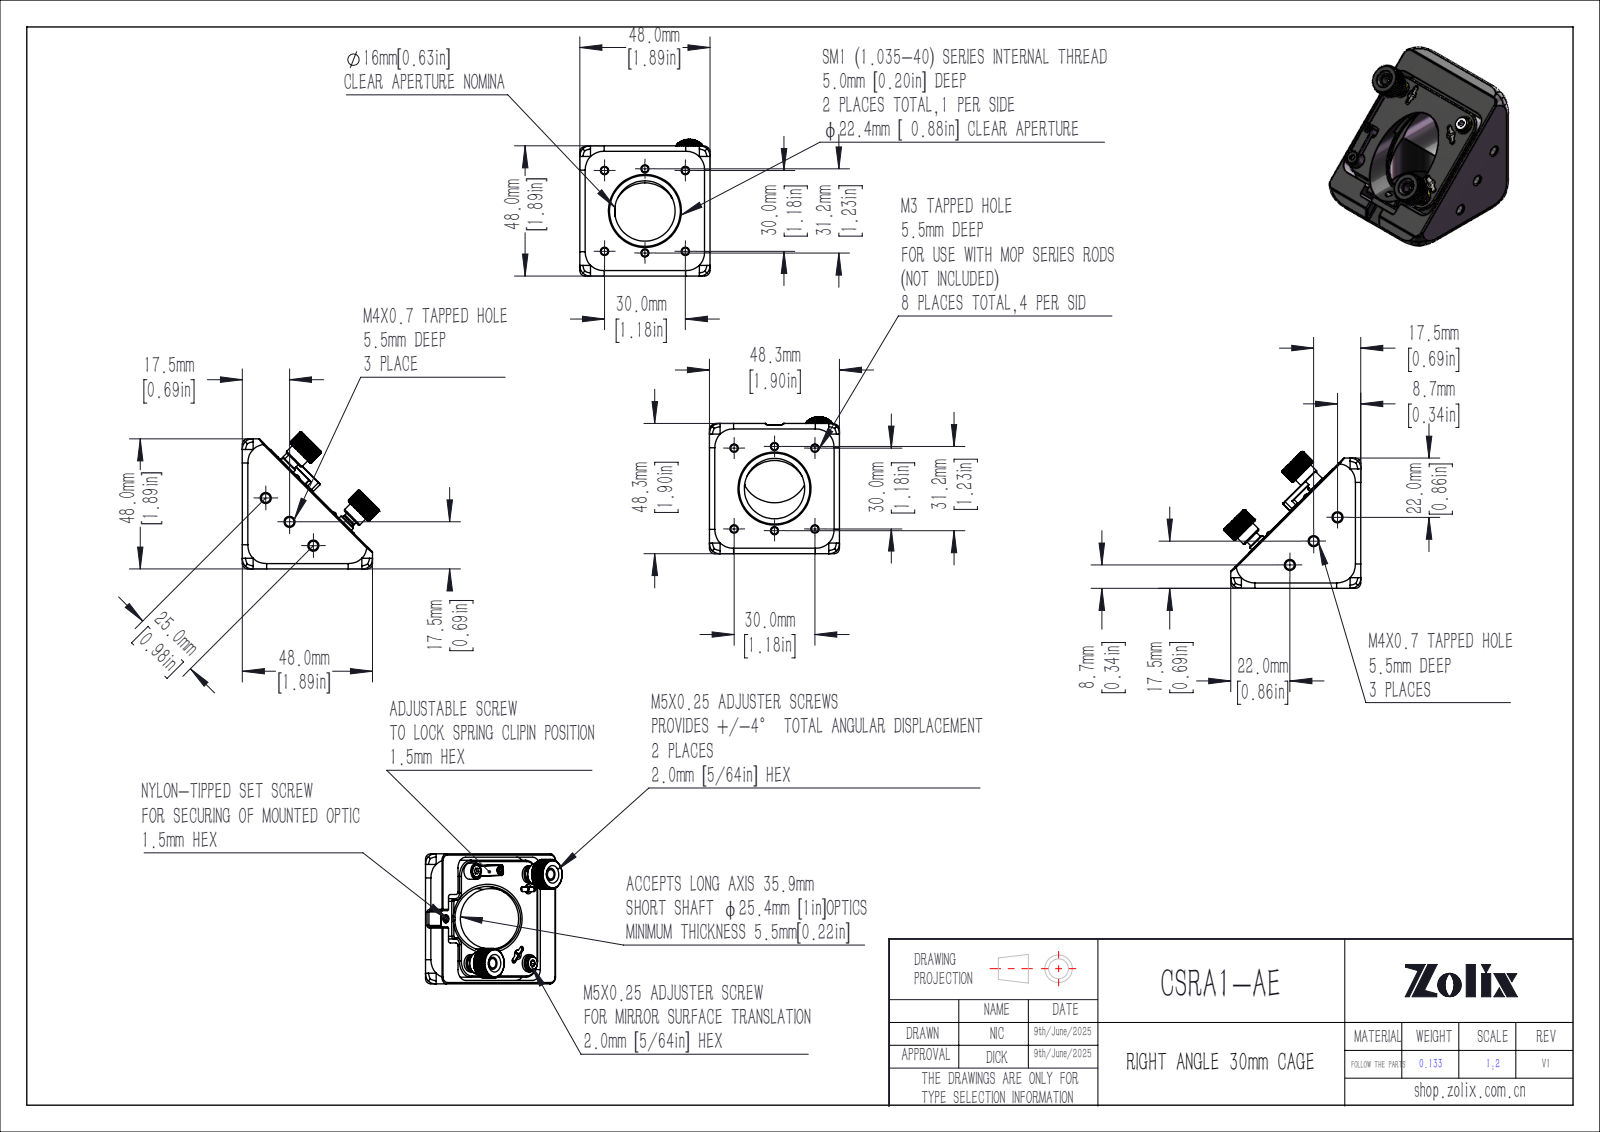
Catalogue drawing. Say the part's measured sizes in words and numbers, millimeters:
The part is named "CSRA1-AE". Its 3-D file was written by "SolidWorks 2020 (CONFIG_CONTROL_DESIGN)". It is 27 solids with 1447 faces: 655 planar, 384 cylindrical and 408 other. Overall it measures 66.65 by 50.69 by 48.3 millimeters. Its volume is 46 334 cubic millimeters and its surface area 24 669 square millimeters. Round holes: 11 of diameter 2.5, 5 of diameter 2.4, 5 of diameter 3.5, 3 of diameter 1.6, 3 of diameter 1.95, 3 of diameter 2.05, 3 of diameter 3.3, 3 of diameter 5, 3 of diameter 6.4, 3 of diameter 7.3, 2 of diameter 2.41, 2 of diameter 4.3. Round bosses or shafts: 4 of diameter 2.5, 3 of diameter 7.1, 3 of diameter 6, 3 of diameter 1.6, 2 of diameter 8, 2 of diameter 3, 2 of diameter 2, 1 of diameter 4.5. Partial cylindrical surfaces (rounded edges, fillets, slot ends): 42 of radius 0.5, 16 of radius 1, 13 of radius 2, 9 of radius 0.2, 6 of radius 0.9, 4 of radius 0.3, 4 of radius 4, 4 of radius 6. The main face-to-face distances are 48.3, 2.39, 1, 6.1, 1.39, 8.49, 7.1, 8.4, 47, 7.01. The hole center spacings are 15.01, 15.62, 21.21, 21.22, 30, 34.09, 34.1, 42.43.
